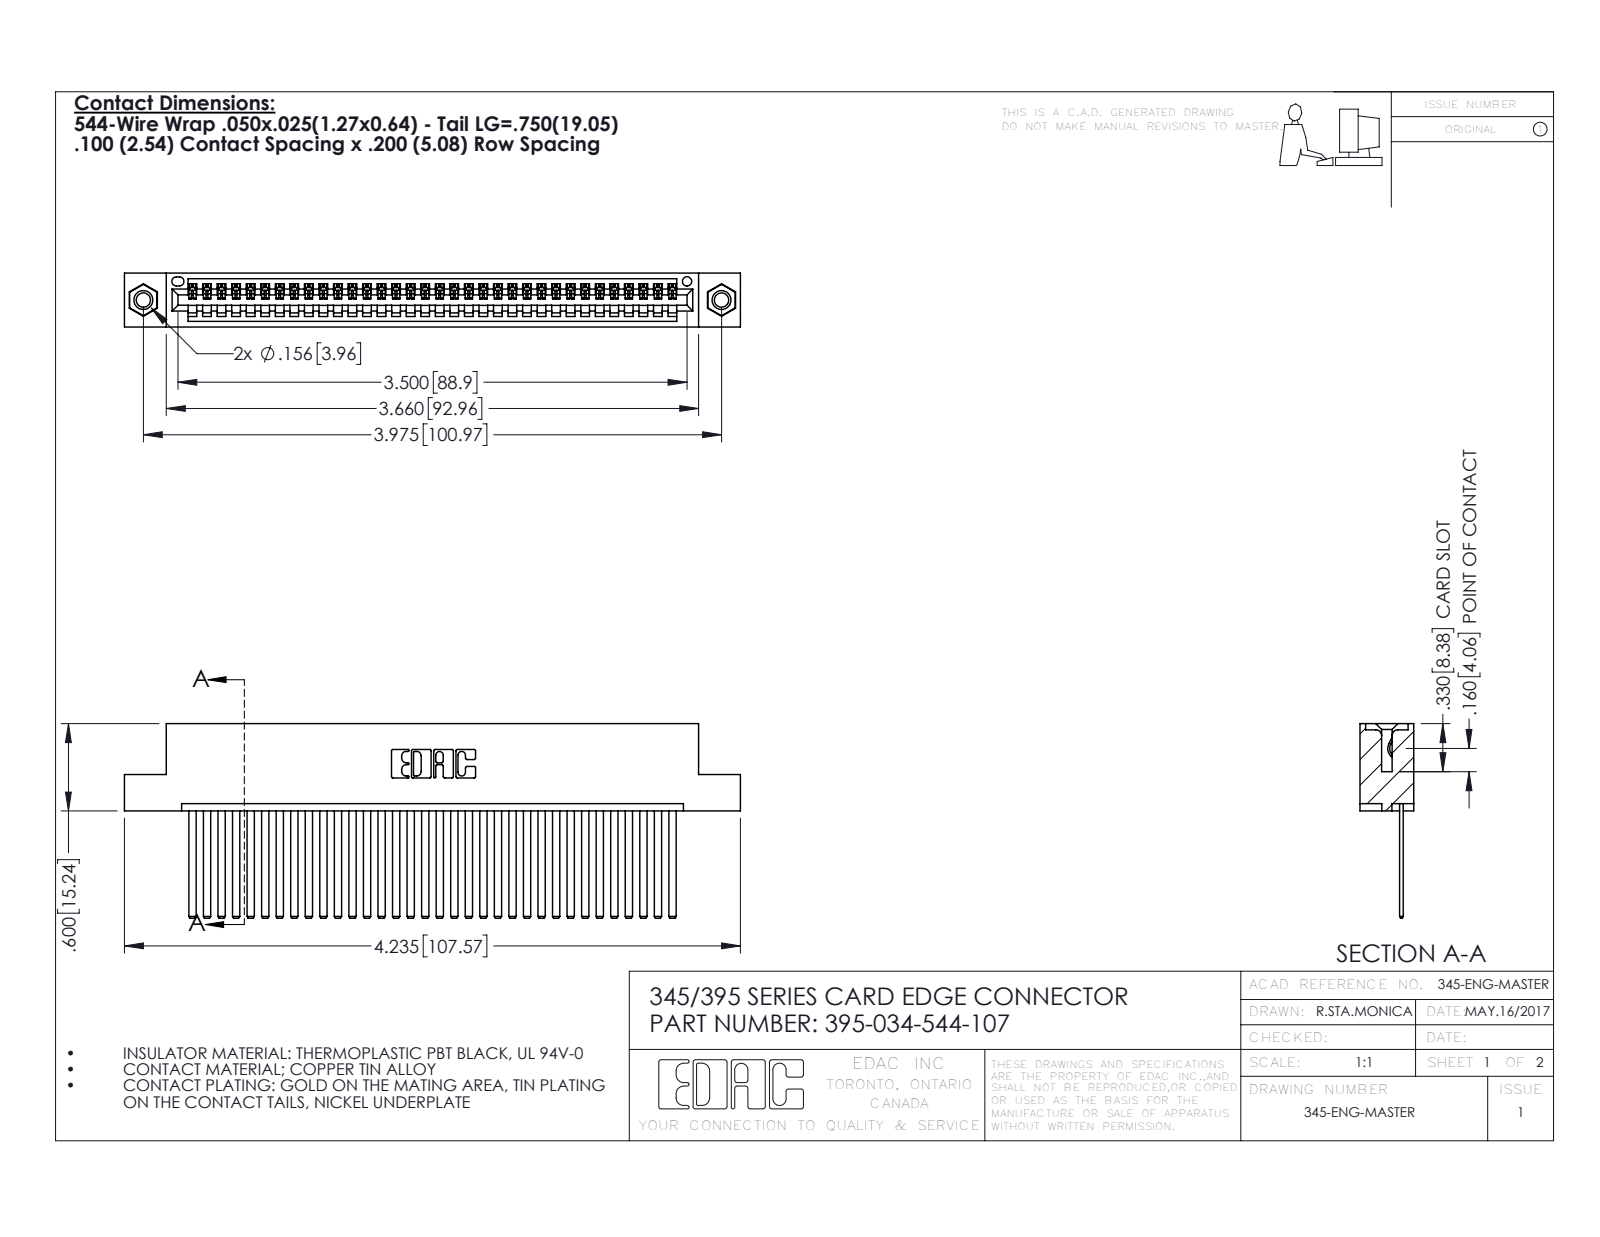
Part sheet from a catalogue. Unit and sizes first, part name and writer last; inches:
Units: inches
Overall size (bounding box): 4.235 × 1.337 × 0.37
Round holes (diameter × count): ⌀0.098 ×2, ⌀0.125 ×2, ⌀0.156 ×2, ⌀0.064 ×1
Round bosses / shafts (diameter × count): ⌀0.155 ×2
Partial cylindrical surfaces — rounded edges, fillets, slot ends (radius × count): R0.006 ×68, R0.01 ×22, R0.007 ×6, R0.031 ×6, R0.026 ×3, R0.031 ×2, R0.04 ×2, R0.014 ×1
Main face-to-face distances: 0.072, 0.298, 0.025, 0.098, 0.272, 0.2, 0.37, 0.225, 0.149, 0.072
Hole centre spacings: 0.27, 3.74, 3.975
Volume: 0.643 in³ · Surface area: 23.41 in²
Bodies: 37 solids, 1954 faces (1336 planar, 602 cylindrical, 16 other)
Part name (STEP PRODUCT): 345 Part_Flush Mounting Lugs - 0.156 Dia-TI; 345-250-001_345-250-005-103; 395-034-544-107; 345-292-001_345-293-144
STEP written by: SolidWorks 2016 (CONFIG_CONTROL_DESIGN)
